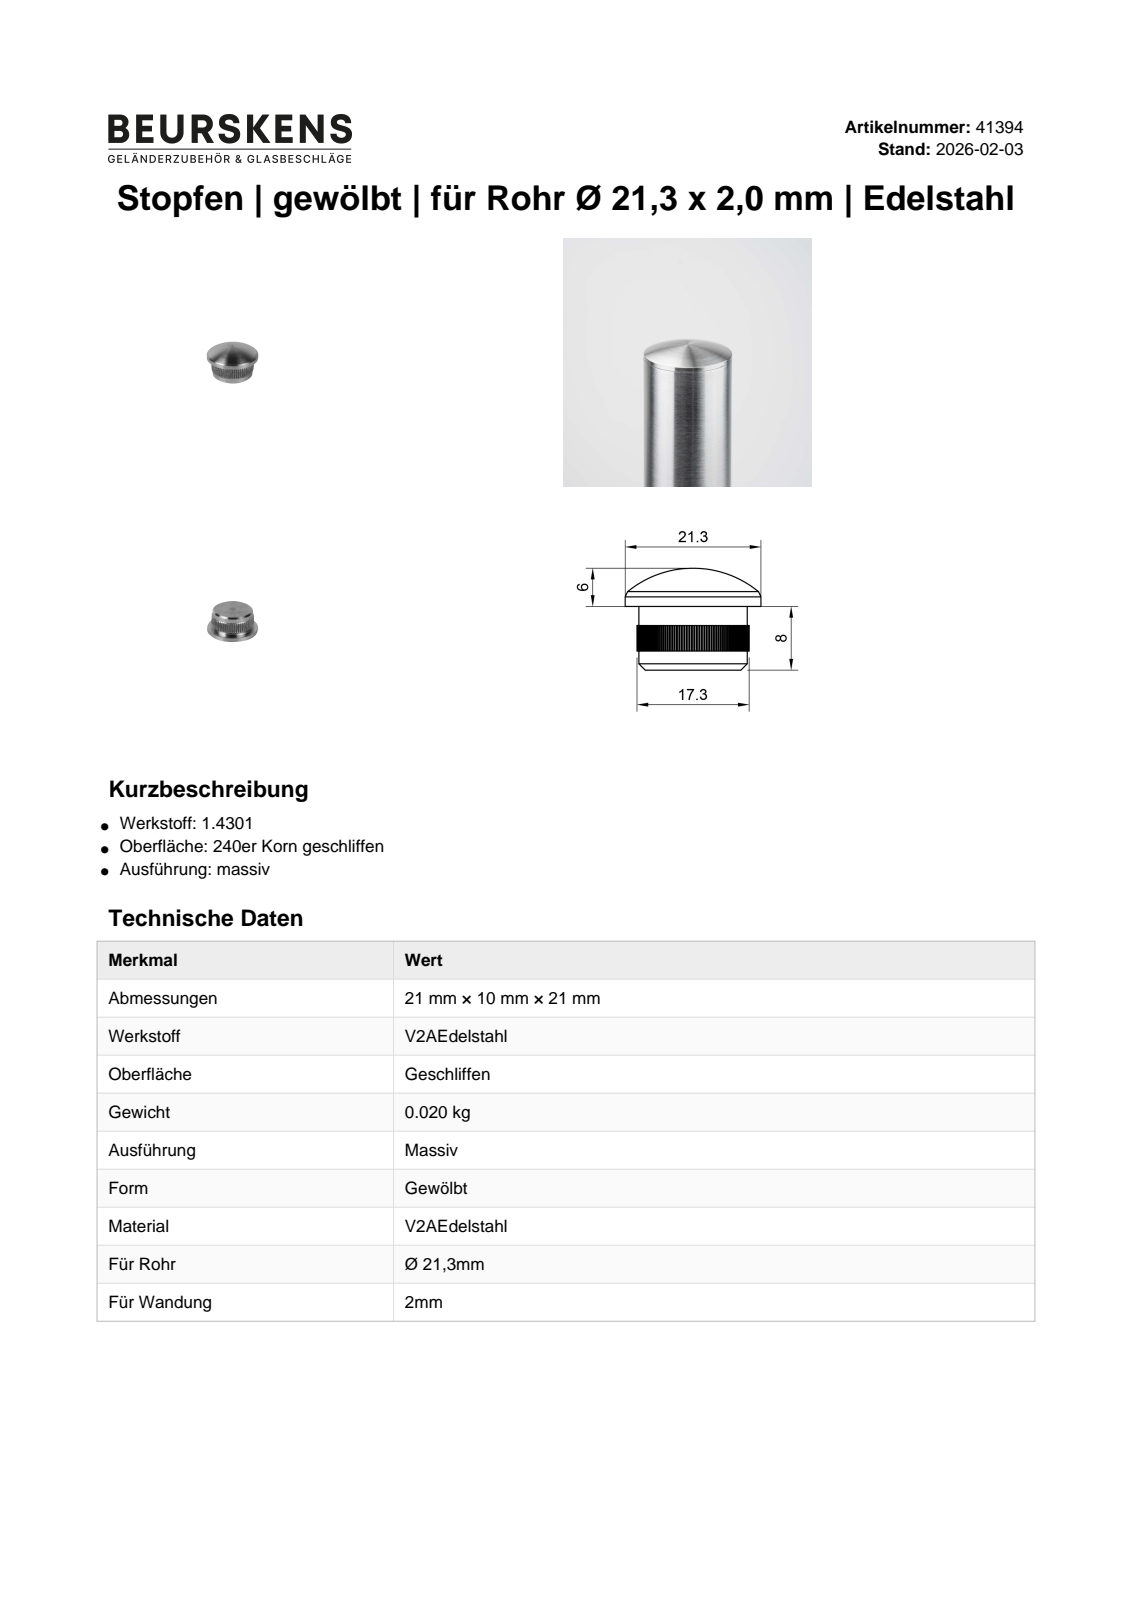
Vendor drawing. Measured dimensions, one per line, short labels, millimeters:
name: 41394
written by: Autodesk Inventor 2022 (AUTOMOTIVE_DESIGN)
unit: mm
bodies: 1 solid, 290 faces (4 planar, 283 cylindrical, 3 other)
size: 21.3 × 21.3 × 16
volume: 3 748 mm³; area: 1 504 mm²
bosses: 1× ⌀21.3, 1× ⌀17
rounds: 140× R0.12, 1× R8.8
face distances: 10, 3, 7, 4
